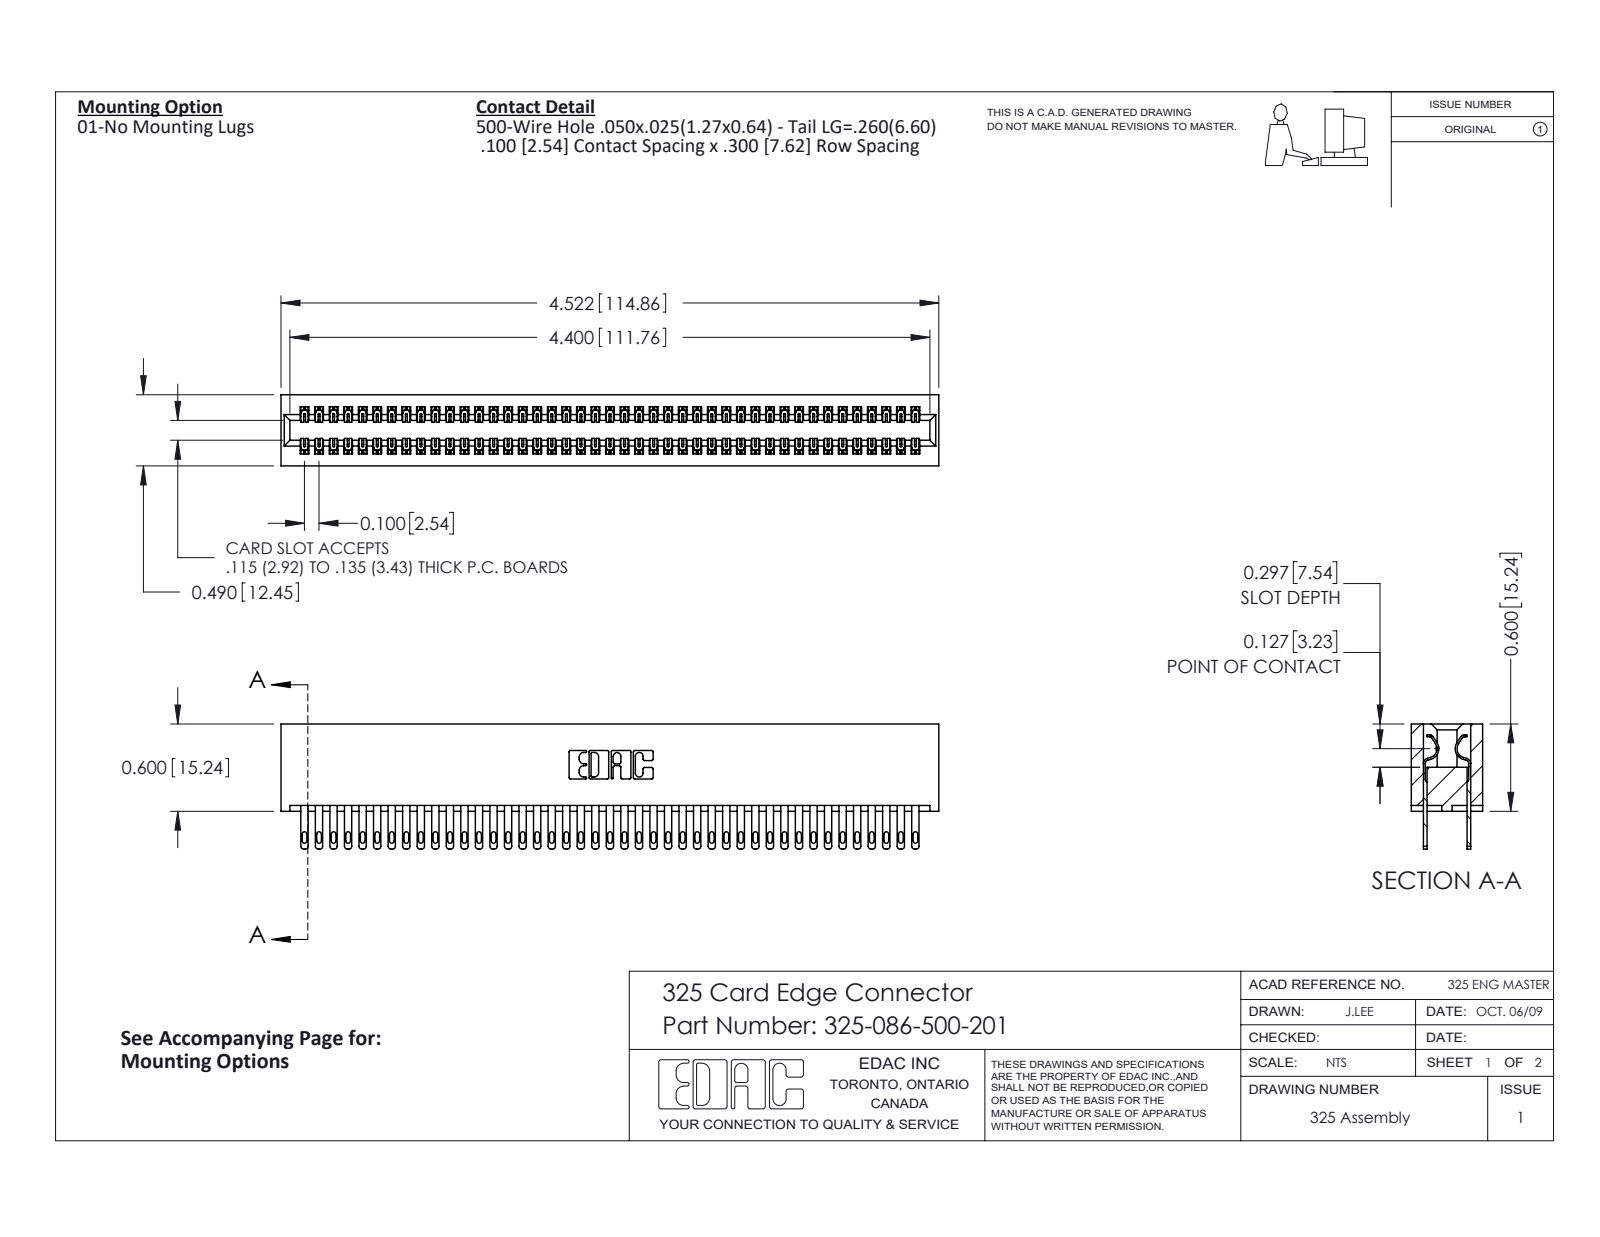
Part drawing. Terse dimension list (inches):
name: 325 Part_Lugless; 325-292-001_325-293-100; 325-086-500-201
written by: SolidWorks 2016 (CONFIG_CONTROL_DESIGN)
unit: in
bodies: 87 solids, 4234 faces (2646 planar, 1588 cylindrical, 0 other)
size: 4.522 × 0.86 × 0.49
volume: 0.958 in³; area: 31.92 in²
rounds: 129× R0.006, 86× R0.016, 86× R0.02, 22× R0.01, 6× R0.007, 6× R0.031, 3× R0.026, 2× R0.014
face distances: 0.083, 0.407, 0.3, 0.107, 0.383, 0.025, 0.325, 0.49, 0.275, 0.56
